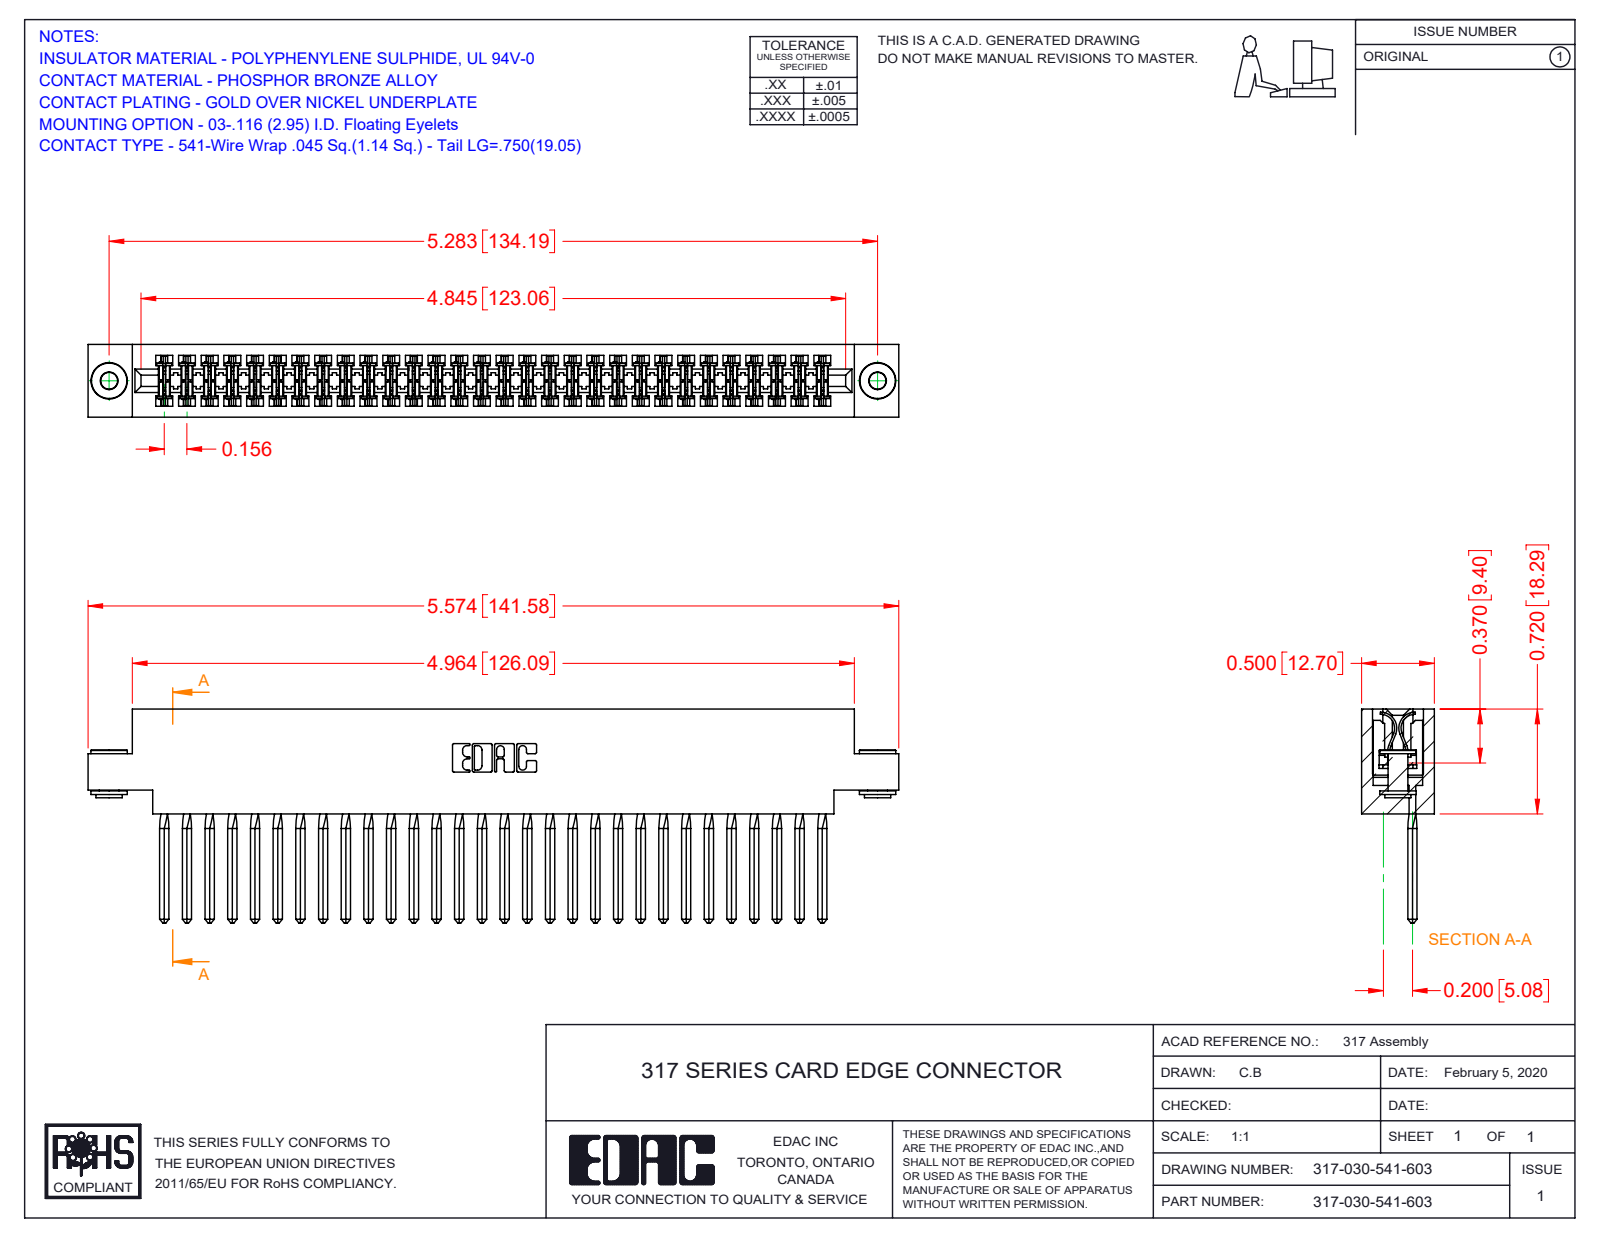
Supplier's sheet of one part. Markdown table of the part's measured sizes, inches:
| quantity | value |
| --- | --- |
| part name | 317-030-541-603; 345-250-002_345-250-002-102; 317-290-002_541; 317 Part_.156 Dia - TH |
| STEP written by | SolidWorks 2016 (CONFIG_CONTROL_DESIGN) |
| units | inches |
| bodies | 33 solids, 4700 faces (3788 planar, 784 cylindrical, 128 other) |
| overall size | 5.574 × 1.47 × 0.5 |
| volume | 1.38 in³ |
| surface area | 49.23 in² |
| round holes (diameter × count) | 0.116 × 2, 0.156 × 2 |
| round bosses / shafts (diameter × count) | 0.25 × 2, 0.18 × 2, 0.136 × 2 |
| partial cylindrical surfaces (radius × count) | 0.015 × 60, 0.01 × 22, 0.007 × 6, 0.031 × 6, 0.026 × 3, 0.095 × 2, 0.1 × 2, 0.11 × 2 |
| main face-to-face distances | 0.5, 0.075, 0.425, 0.35, 0.11, 0.195, 0.72, 0.115, 0.211, 0.289 |
| hole center spacings | 5.283 |
